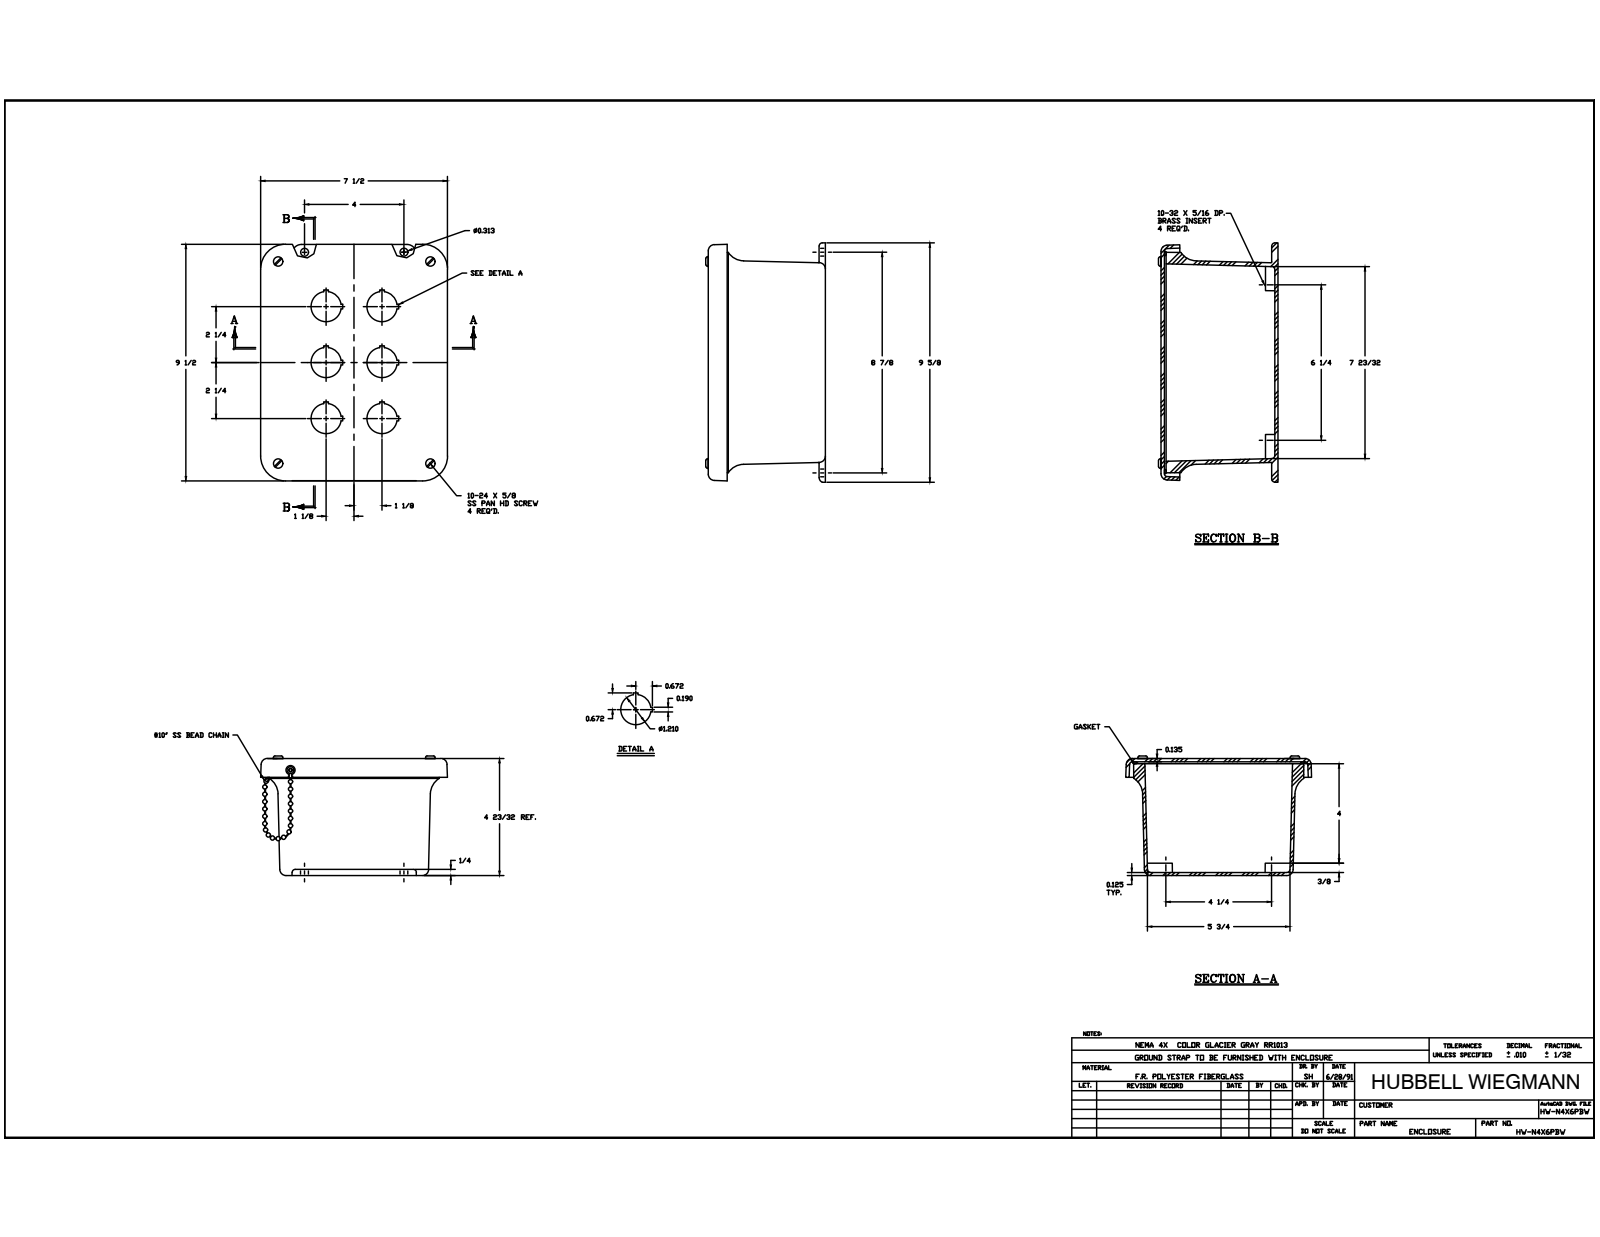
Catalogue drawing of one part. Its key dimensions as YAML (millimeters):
part_name: "WPF6PBW BOX; 10-32 X0.3125 DP BRASS INSERT; 10-24X0.50 DP BRASS INSERT; WPF6PBW CVR (+6 more)"
step_written_by: "Autodesk Inventor 2014 (AUTOMOTIVE_DESIGN)"
units: millimeters
bodies: {solids: 19, faces: 637, planar: 236, cylindrical: 213, other: 188}
overall_size: [245.13, 189.88, 122.86]
volume: 743852
surface_area: 363051
round_holes:
  - {diameter: 30.73, count: 6}
  - {diameter: 3.68, count: 4}
  - {diameter: 3.96, count: 4}
  - {diameter: 5.56, count: 4}
  - {diameter: 6.35, count: 4}
  - {diameter: 7.14, count: 4}
  - {diameter: 7.94, count: 4}
  - {diameter: 2.64, count: 1}
  - {diameter: 3.56, count: 1}
round_bosses_or_shafts:
  - {diameter: 9.42, count: 4}
  - {diameter: 7.14, count: 4}
  - {diameter: 5.54, count: 4}
  - {diameter: 4.5, count: 4}
  - {diameter: 0.74, count: 2}
  - {diameter: 9.4, count: 1}
partial_cylinders:
  - {radius: 0.79, count: 36}
  - {radius: 0.3, count: 16}
  - {radius: 0.83, count: 16}
  - {radius: 3.17, count: 12}
  - {radius: 6.35, count: 12}
  - {radius: 2.79, count: 4}
  - {radius: 7.98, count: 4}
  - {radius: 19.05, count: 4}
face_to_face_distances: [3.43, 116.43, 119.86, 3.17, 113.26, 116.69, 114.3, 111.13, 2.13, 5.56]
hole_center_spacings: [57.15, 33.49, 184.11, 192.12, 33.75, 83.34, 114.52, 158.75]
